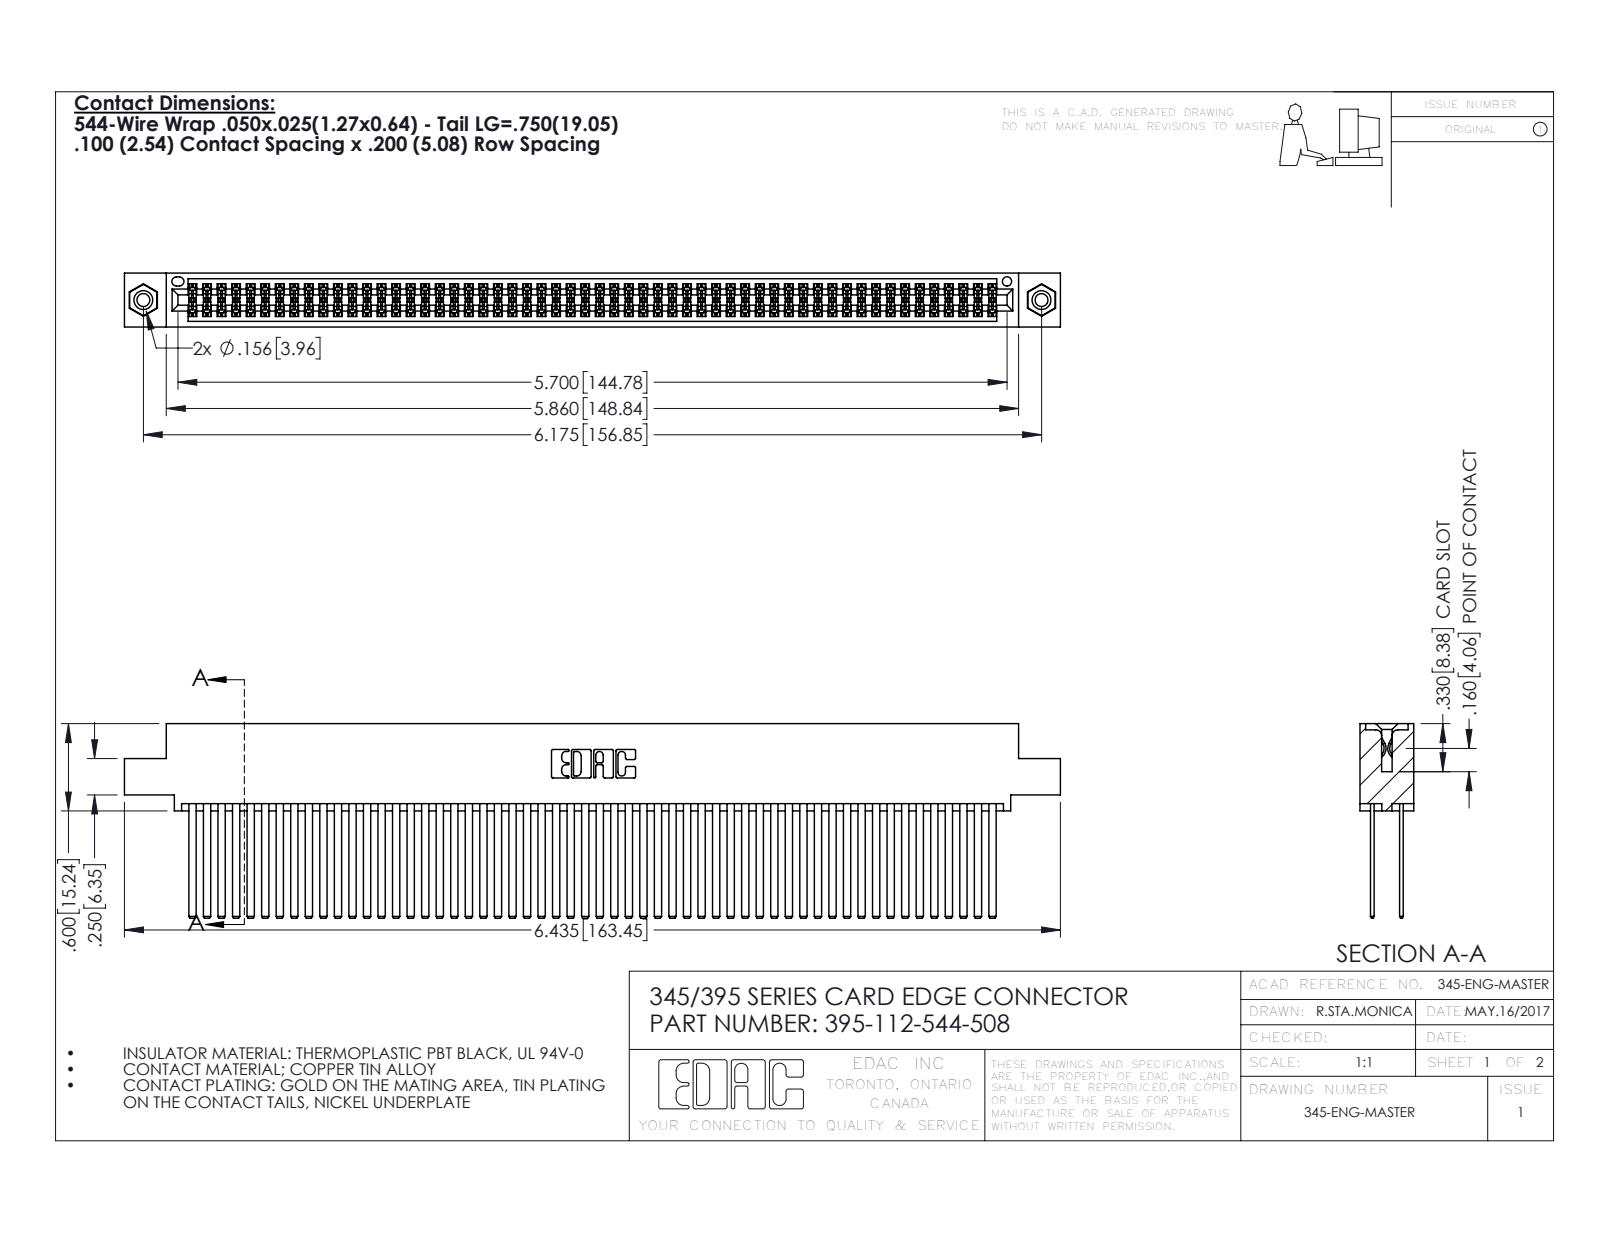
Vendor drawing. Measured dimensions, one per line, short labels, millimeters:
name: 345 Part_0.110 Offset - 0.156 Dia-TI; 345-250-001_345-250-003-102; 345-292-001_345-293-144; 395-112-544-508
written by: SolidWorks 2016 (CONFIG_CONTROL_DESIGN)
unit: mm
bodies: 115 solids, 5118 faces (3364 planar, 1738 cylindrical, 16 other)
size: 163.4 × 34 × 9.4
volume: 17 500 mm³; area: 30 850 mm²
holes: 2× ⌀2.3, 2× ⌀3.2, 2× ⌀4, 1× ⌀1.6
bosses: 2× ⌀3.9
rounds: 168× R0.2, 22× R0.3, 6× R0.2, 6× R0.8, 3× R0.7, 2× R0.4, 2× R0.5, 2× R0.6
face distances: 5.1, 0.6, 1.8, 2.5, 6.9, 7.6, 5.7, 4.4, 9.4, 1.3
hole spacings: 6.9, 150.9, 156.8
